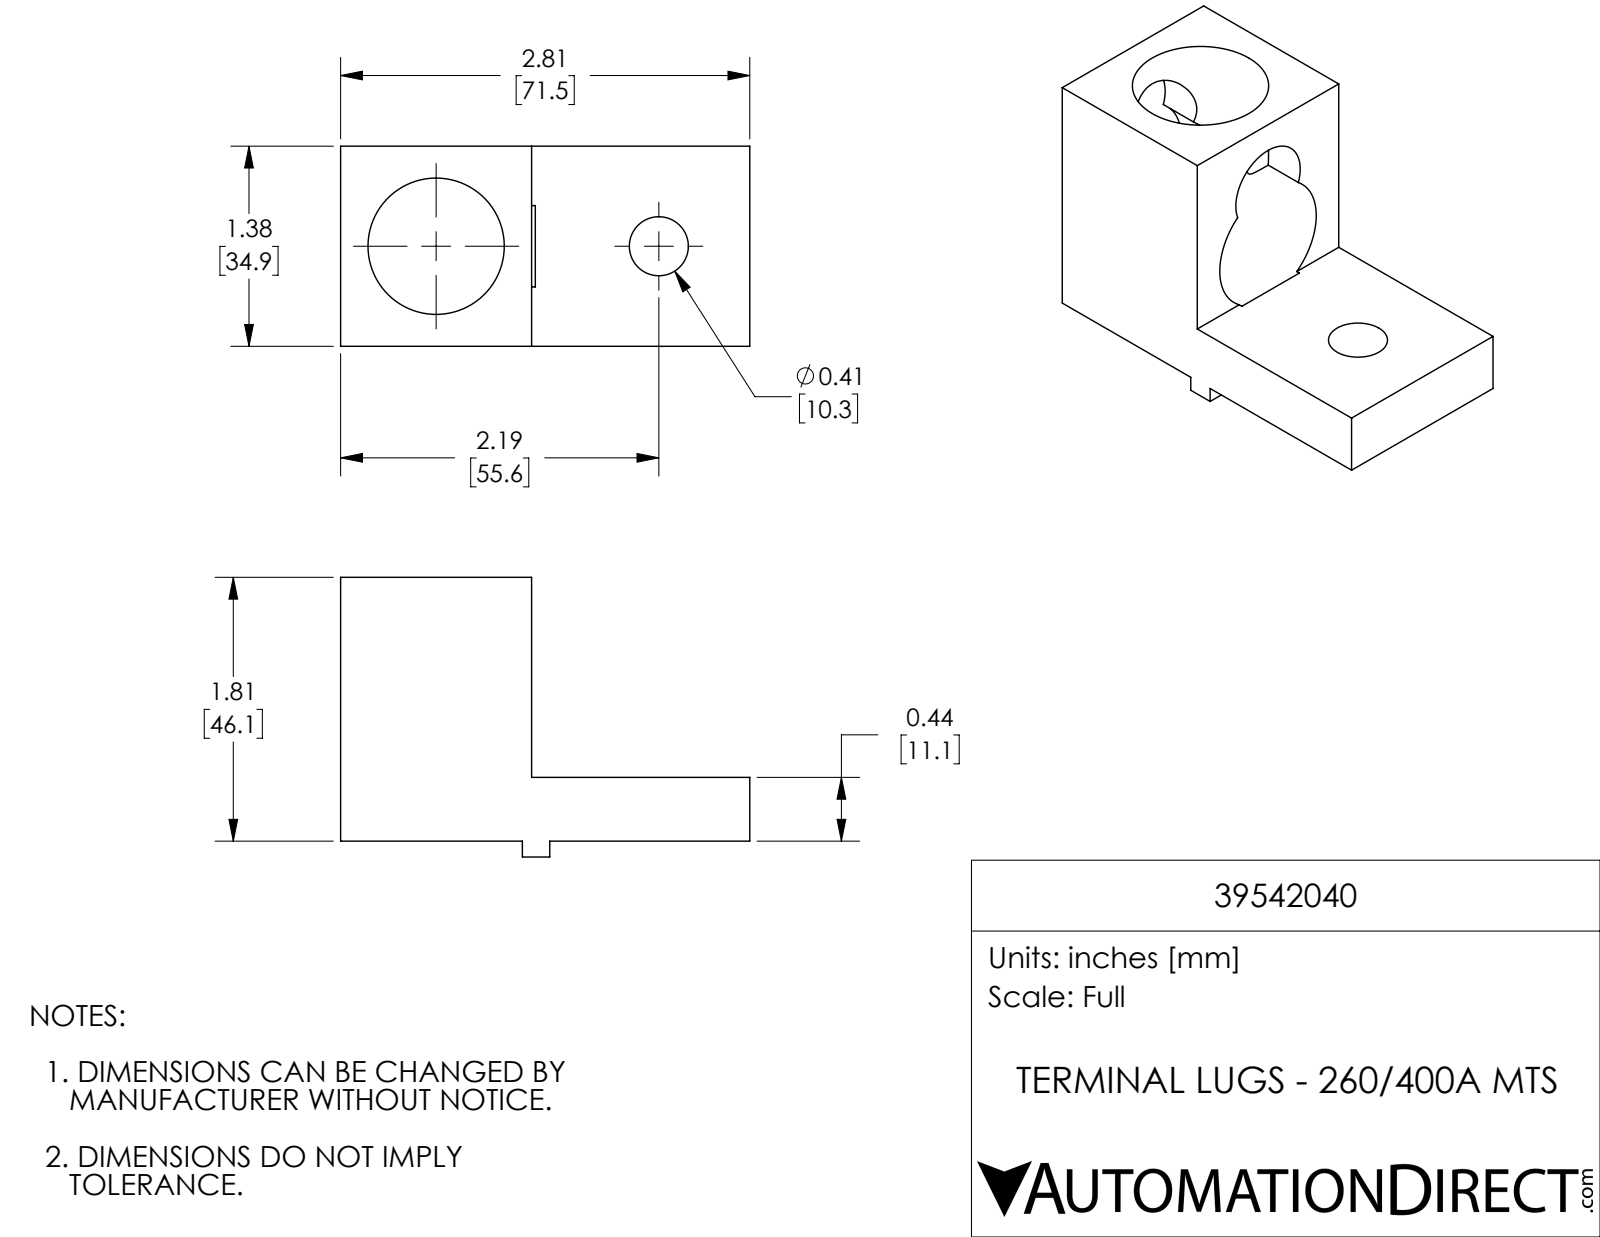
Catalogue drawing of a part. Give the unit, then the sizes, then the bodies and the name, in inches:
Units: inches
Overall size (bounding box): 2.813 × 1.922 × 1.375
Round holes (diameter × count): ⌀0.406 ×1, ⌀0.937 ×1
Partial cylindrical surfaces — rounded edges, fillets, slot ends (radius × count): R0.313 ×1, R0.469 ×1
Main face-to-face distances: 1.375, 0.438, 1.813, 1.375, 1.313, 2.813, 1.5, 0.109, 0.547, 1.922
Hole centre spacings: 1.531
Volume: 2.749 in³ · Surface area: 22.08 in²
Bodies: 1 solid, 22 faces (13 planar, 9 cylindrical, 0 other)
Part name (STEP PRODUCT): 39542040
STEP written by: SolidWorks 2017 (AUTOMOTIVE_DESIGN)
